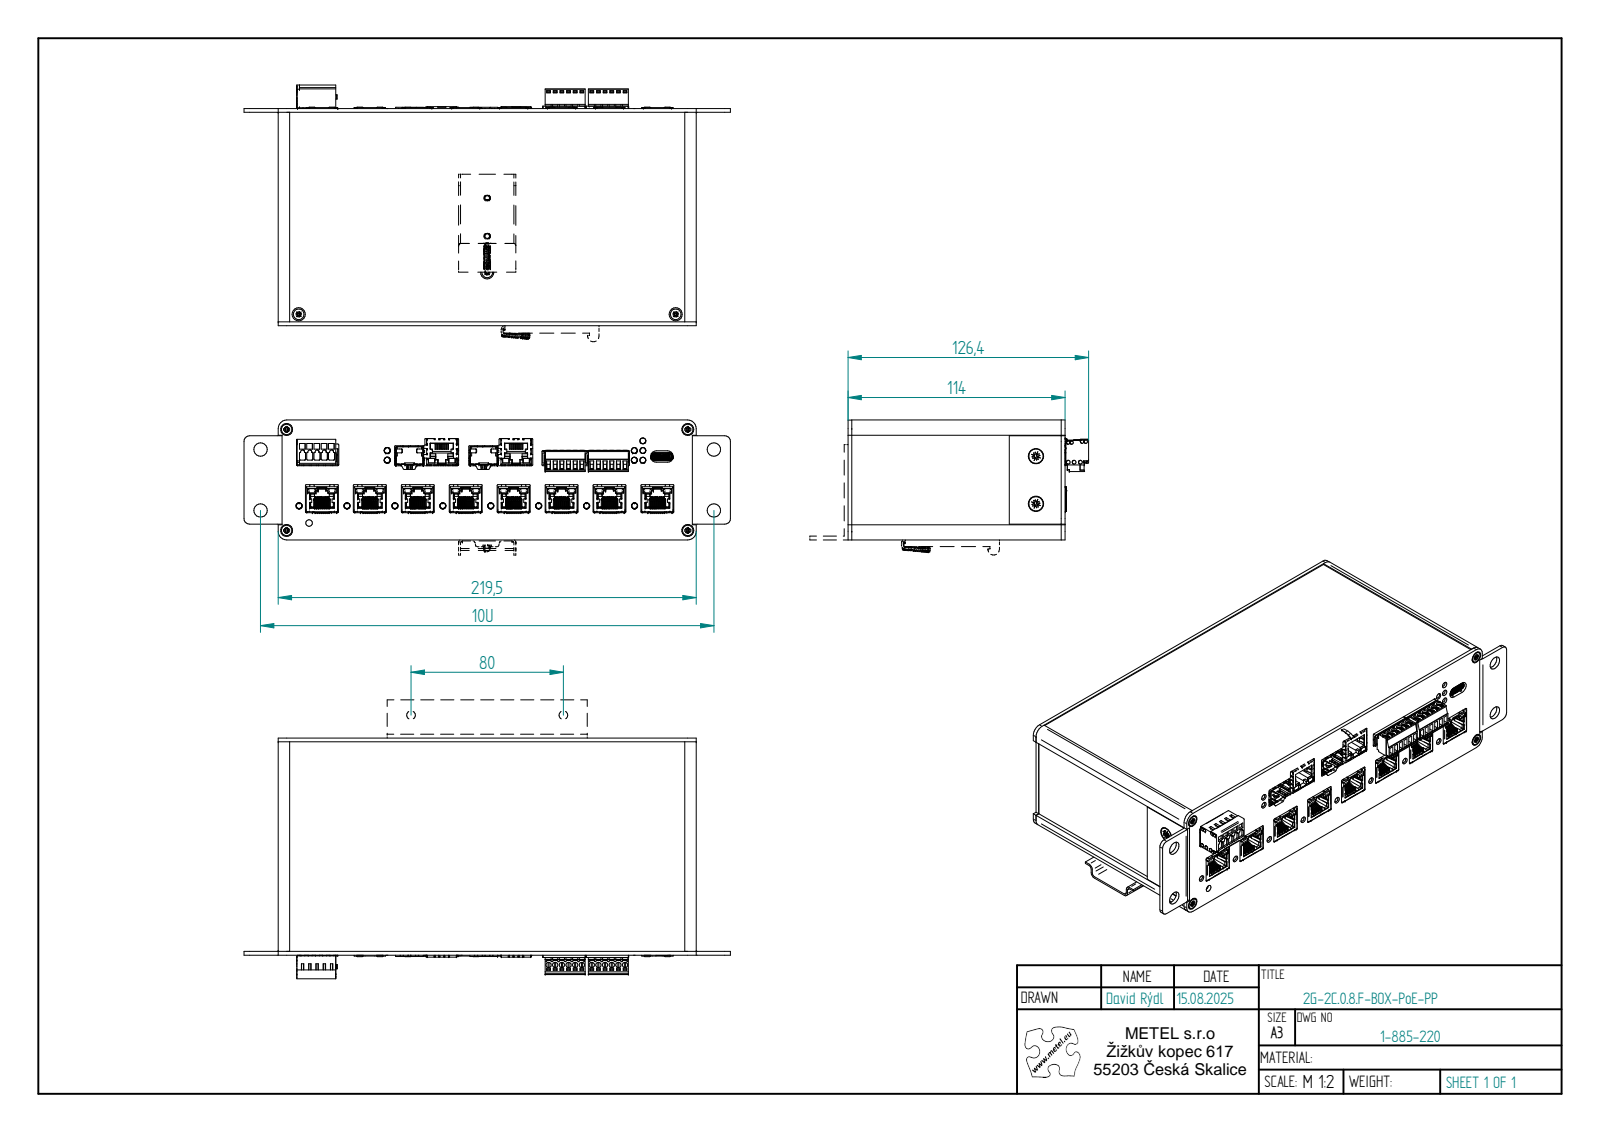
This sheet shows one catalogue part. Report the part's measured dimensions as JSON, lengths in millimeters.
{"part_name": "2G-2C.0.8.F; Profil 210-2C.0.8-zak; 1-885-220-20241105-005-2C.0.8.F-Predni; 734-205 (+8 more)", "step_written_by": "Solid Edge (AP242_MANAGED_MODEL_BASED_3D_ENGINEERING_MIM_LF)", "units": "millimeters", "bodies": {"solids": 149, "faces": 20951, "planar": 14663, "cylindrical": 4731, "other": 1557}, "overall_size": [255.5, 146.35, 73.41], "volume_mm3": 309180, "surface_area_mm2": 313308, "round_holes": [[1, 30], [2, 24], [1.5, 17], [3.2, 17], [3.3, 13], [1.9, 12], [2.1, 12], [2.8, 12], [3.5, 9], [2.46, 6], [0.45, 4], [2.7, 4]], "round_bosses_or_shafts": [[1.8, 14], [2.9, 12], [3, 10], [5.5, 4], [5.6, 3], [2.63, 3], [2, 3], [7.5, 2]], "partial_cylinders_radius": [[0.1, 214], [0.25, 197], [0.24, 144], [0.2, 129], [1.02, 128], [0.5, 115], [0.38, 85], [0.13, 84]], "face_to_face_distances": [2.88, 59.12, 2, 112, 62, 56.24, 4, 114, 110, 211.5], "hole_center_spacings": [25.17, 50.34, 75.51, 100.68, 2.54, 75.52, 100.69, 125.85]}
